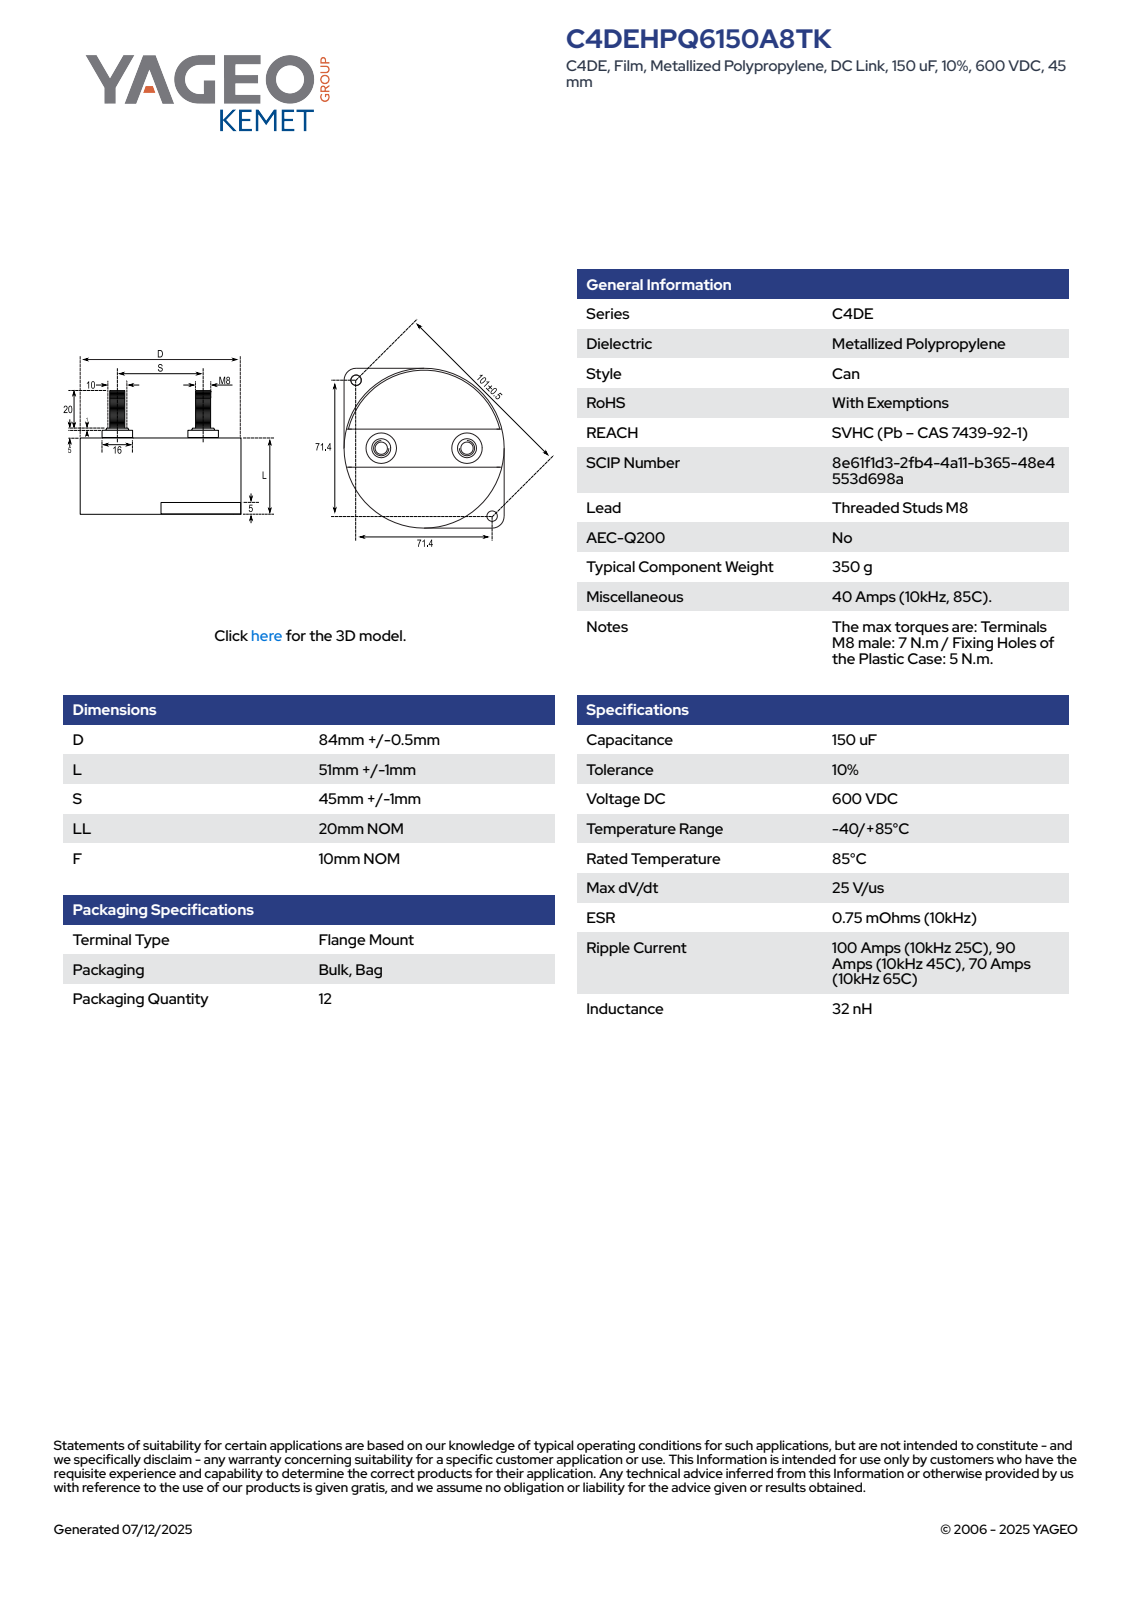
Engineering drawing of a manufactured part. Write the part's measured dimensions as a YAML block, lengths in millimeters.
part_name: "CFP_C44DE_84X51_D84.5L52S46LL20"
step_written_by: "SolidWorks 2021 (AUTOMOTIVE_DESIGN)"
units: millimeters
bodies: {solids: 1, faces: 103, planar: 37, cylindrical: 31, other: 35}
overall_size: [84.51, 84.5, 78]
volume: 299186
surface_area: 28237
round_holes:
  - {diameter: 5.5, count: 2}
round_bosses_or_shafts:
  - {diameter: 16, count: 2}
  - {diameter: 10, count: 2}
  - {diameter: 8, count: 2}
  - {diameter: 84.5, count: 1}
  - {diameter: 80, count: 1}
partial_cylinders:
  - {radius: 10, count: 2}
  - {radius: 42.26, count: 1}
face_to_face_distances: [52, 5, 47, 84.5, 57, 78, 73, 26, 21, 58]
hole_center_spacings: [101.51]
